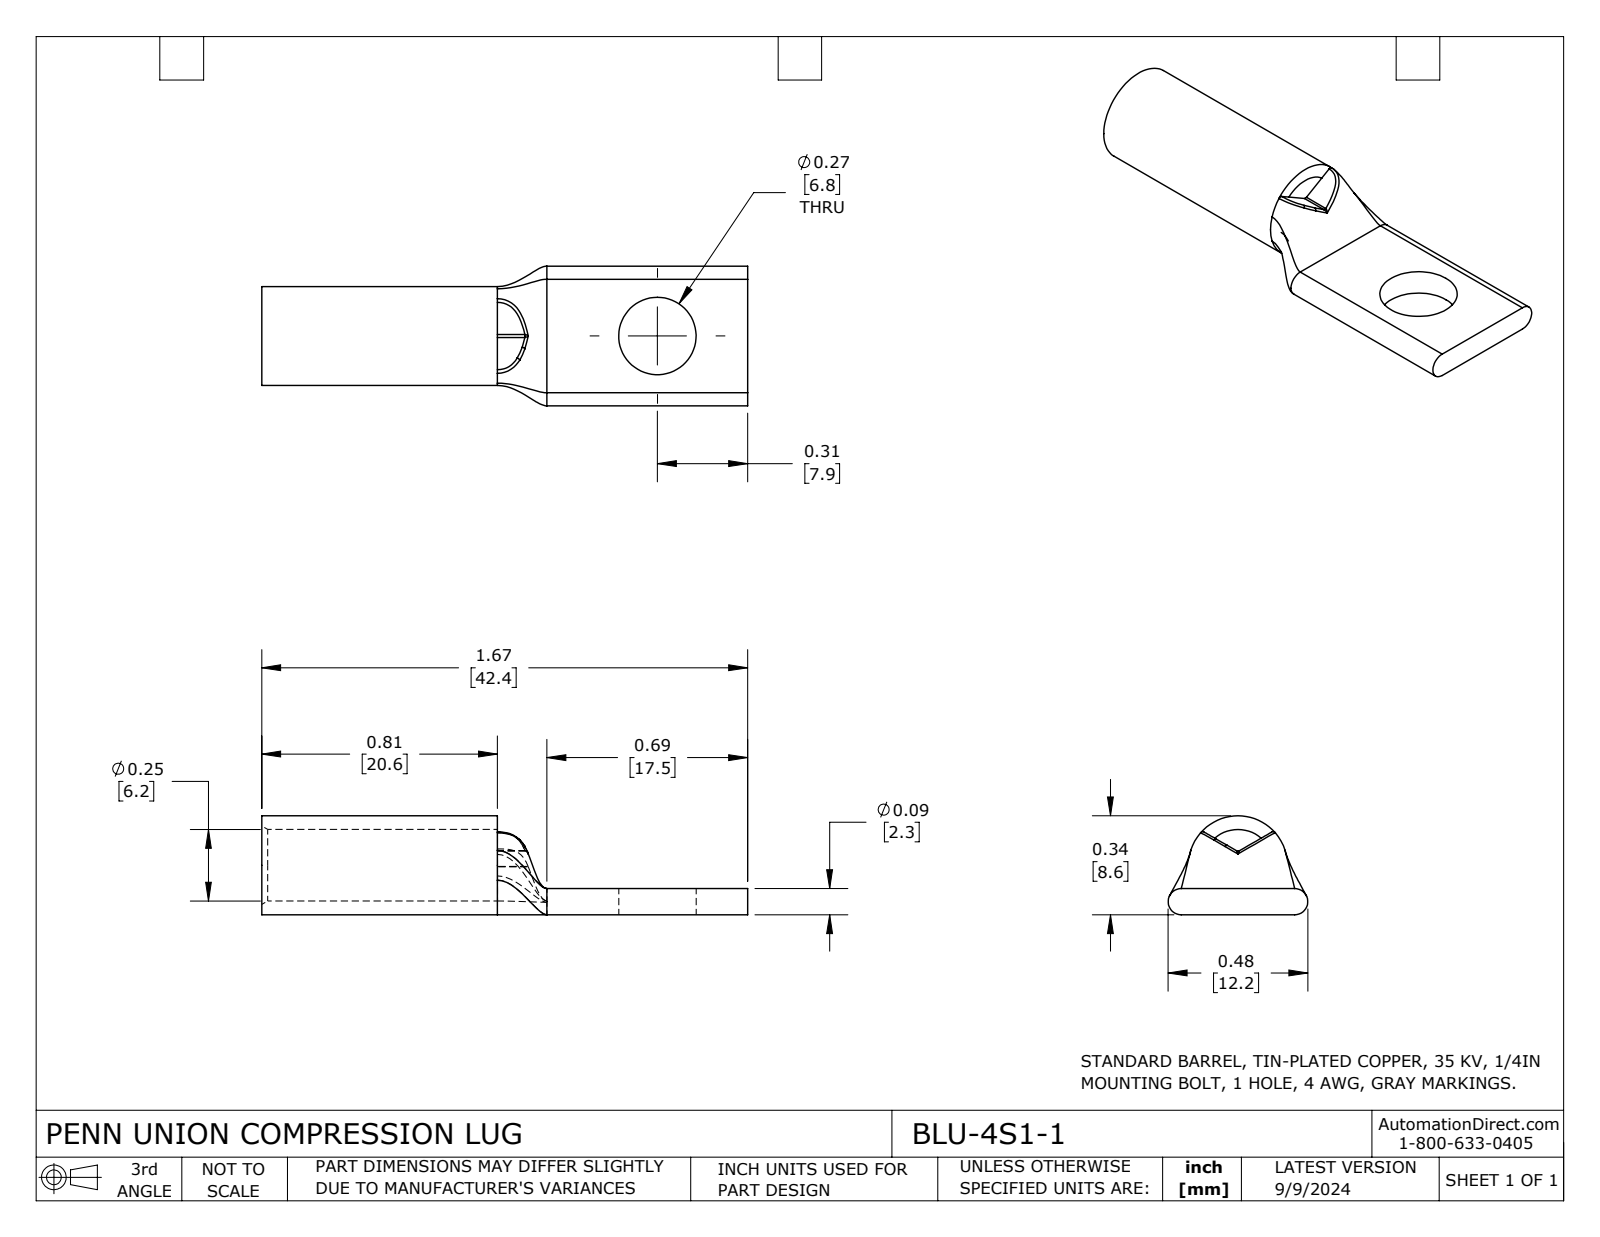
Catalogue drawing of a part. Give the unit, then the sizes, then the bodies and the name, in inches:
Units: inches
Overall size (bounding box): 1.67 × 0.48 × 0.34
Round holes (diameter × count): ⌀0.246 ×1, ⌀0.266 ×1
Round bosses / shafts (diameter × count): ⌀0.34 ×1
Partial cylindrical surfaces — rounded edges, fillets, slot ends (radius × count): R0.01 ×2, R0.045 ×2
Main face-to-face distances: 0.09, 1.67, 0.81, 0.86, 0.047, 0.98, 0.17, 0.69
Volume: 0.065 in³ · Surface area: 2.667 in²
Bodies: 1 solid, 37 faces (11 planar, 11 cylindrical, 15 other)
Part name (STEP PRODUCT): BLU-4S1-1
STEP written by: SolidWorks 2023 (CONFIG_CONTROL_DESIGN)
